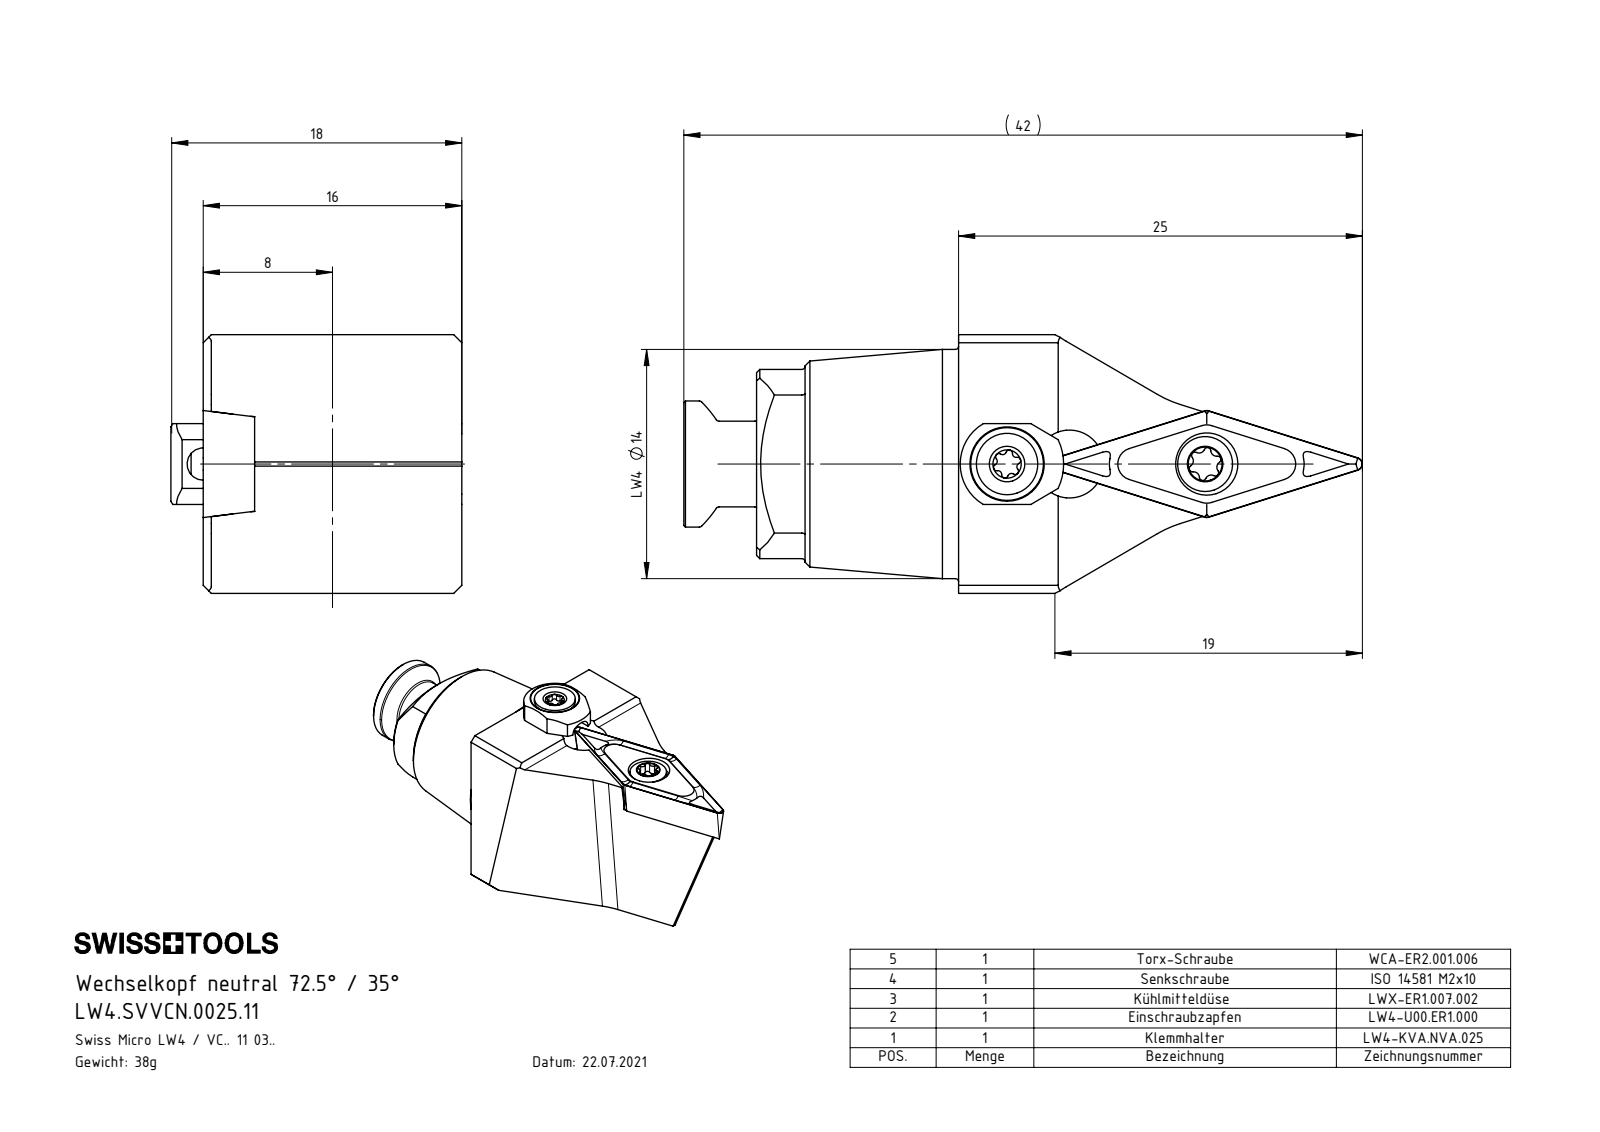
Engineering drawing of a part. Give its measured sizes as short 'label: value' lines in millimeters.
name: LW4-KVA.NVA.025_A; ISO 14581 - M2x10; VCGT110304; WCA-ER2.001.006_A (+3 more)
written by: SolidWorks 2022 (CONFIG_CONTROL_DESIGN)
unit: mm
bodies: 6 solids, 264 faces (71 planar, 84 cylindrical, 109 other)
size: 41.98 × 18 × 16
volume: 4 653 mm³; area: 3 156 mm²
holes: 2× ⌀2, 1× ⌀1.6, 1× ⌀2.05, 1× ⌀2.5, 1× ⌀2.8, 1× ⌀3, 1× ⌀3.85, 1× ⌀4.2, 1× ⌀5.5
bosses: 1× ⌀14.17, 1× ⌀7.7, 1× ⌀6, 1× ⌀5.3, 1× ⌀5, 1× ⌀3.8, 1× ⌀3.4, 1× ⌀2.5
rounds: 8× R0.2, 6× R0.21, 6× R0.24, 4× R0.36, 2× R0.36, 2× R7, 1× R0.5, 1× R1
face distances: 16, 12.82, 3.18, 15.5, 2.68, 0.5, 7.5, 2, 12.5, 4
hole spacings: 3.86, 8.39, 8.5, 12.25, 12.36
